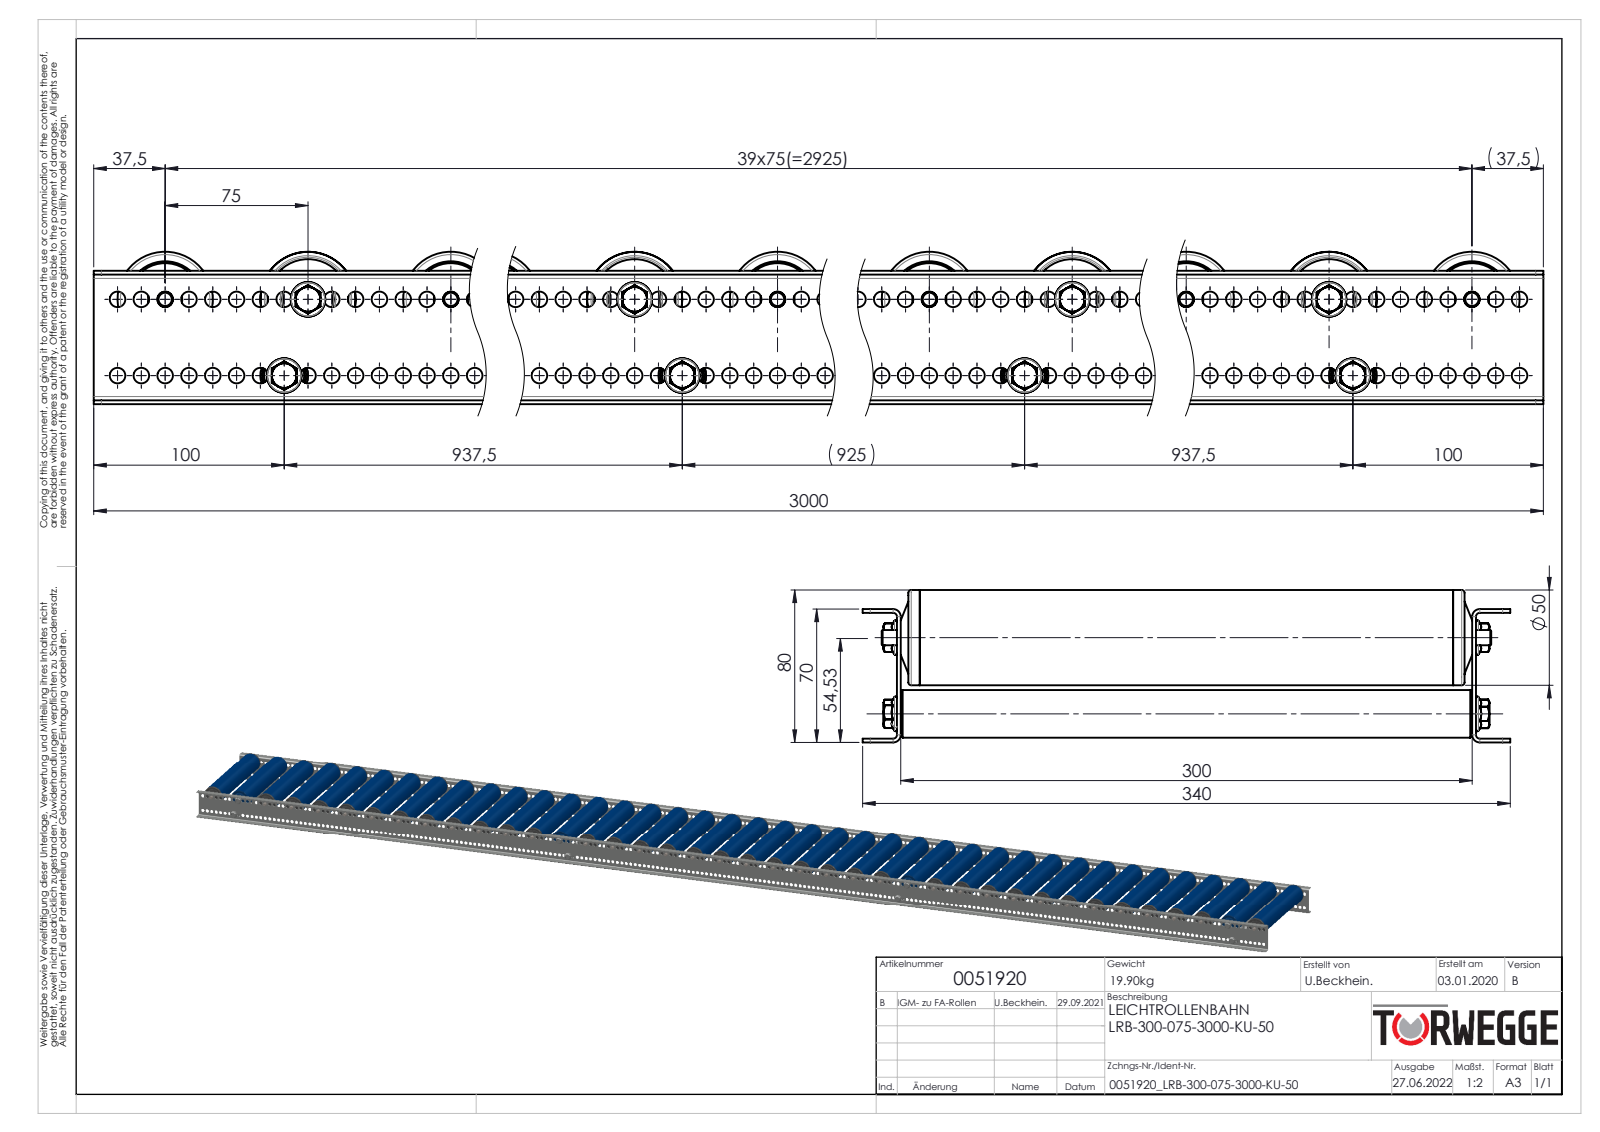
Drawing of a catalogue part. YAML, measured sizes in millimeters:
part_name: "S100994_Sperrzahnschraube_M08x16-8.8-A2K; KUT100-50x2,8-KB-A8-FA_KFG_0034513_KUT100-50x2,8-KB-A8-FA-EL=300; 0017015_Tragrollenrohr-Ø50x2,8KU_KFG_0017015_L=280; Profil_LRB-20x70x20x2_KFG_S109080_U-PROFIL-20-70-20-2-LRB-L=3000 (+8 more)"
step_written_by: "SolidWorks 2020 (AUTOMOTIVE_DESIGN)"
units: millimeters
bodies: {solids: 634, faces: 12220, planar: 3052, cylindrical: 5720, other: 3448}
overall_size: [3000, 340, 80]
volume: 8911000
surface_area: 6768000
round_holes:
  - {diameter: 8.2, count: 478}
  - {diameter: 7.6, count: 36}
  - {diameter: 8, count: 36}
  - {diameter: 25, count: 36}
  - {diameter: 30, count: 36}
  - {diameter: 35, count: 36}
  - {diameter: 39.4, count: 36}
  - {diameter: 40, count: 36}
  - {diameter: 6.8, count: 8}
  - {diameter: 12, count: 4}
  - {diameter: 12.1, count: 4}
  - {diameter: 16, count: 4}
round_bosses_or_shafts:
  - {diameter: 50, count: 40}
  - {diameter: 44.4, count: 36}
  - {diameter: 38, count: 36}
  - {diameter: 36, count: 36}
  - {diameter: 33, count: 36}
  - {diameter: 22, count: 36}
  - {diameter: 21, count: 36}
  - {diameter: 25, count: 8}
partial_cylinders:
  - {radius: 0.6, count: 72}
  - {radius: 0.75, count: 72}
  - {radius: 2.45, count: 72}
  - {radius: 4.87, count: 36}
  - {radius: 7, count: 36}
  - {radius: 4, count: 8}
  - {radius: 2, count: 4}
  - {radius: 2.5, count: 4}
face_to_face_distances: [2, 302, 68, 300, 304, 70, 66, 292, 12, 6]
hole_center_spacings: [12.5, 25, 37.5, 50, 62.5, 75, 87.5, 100]
